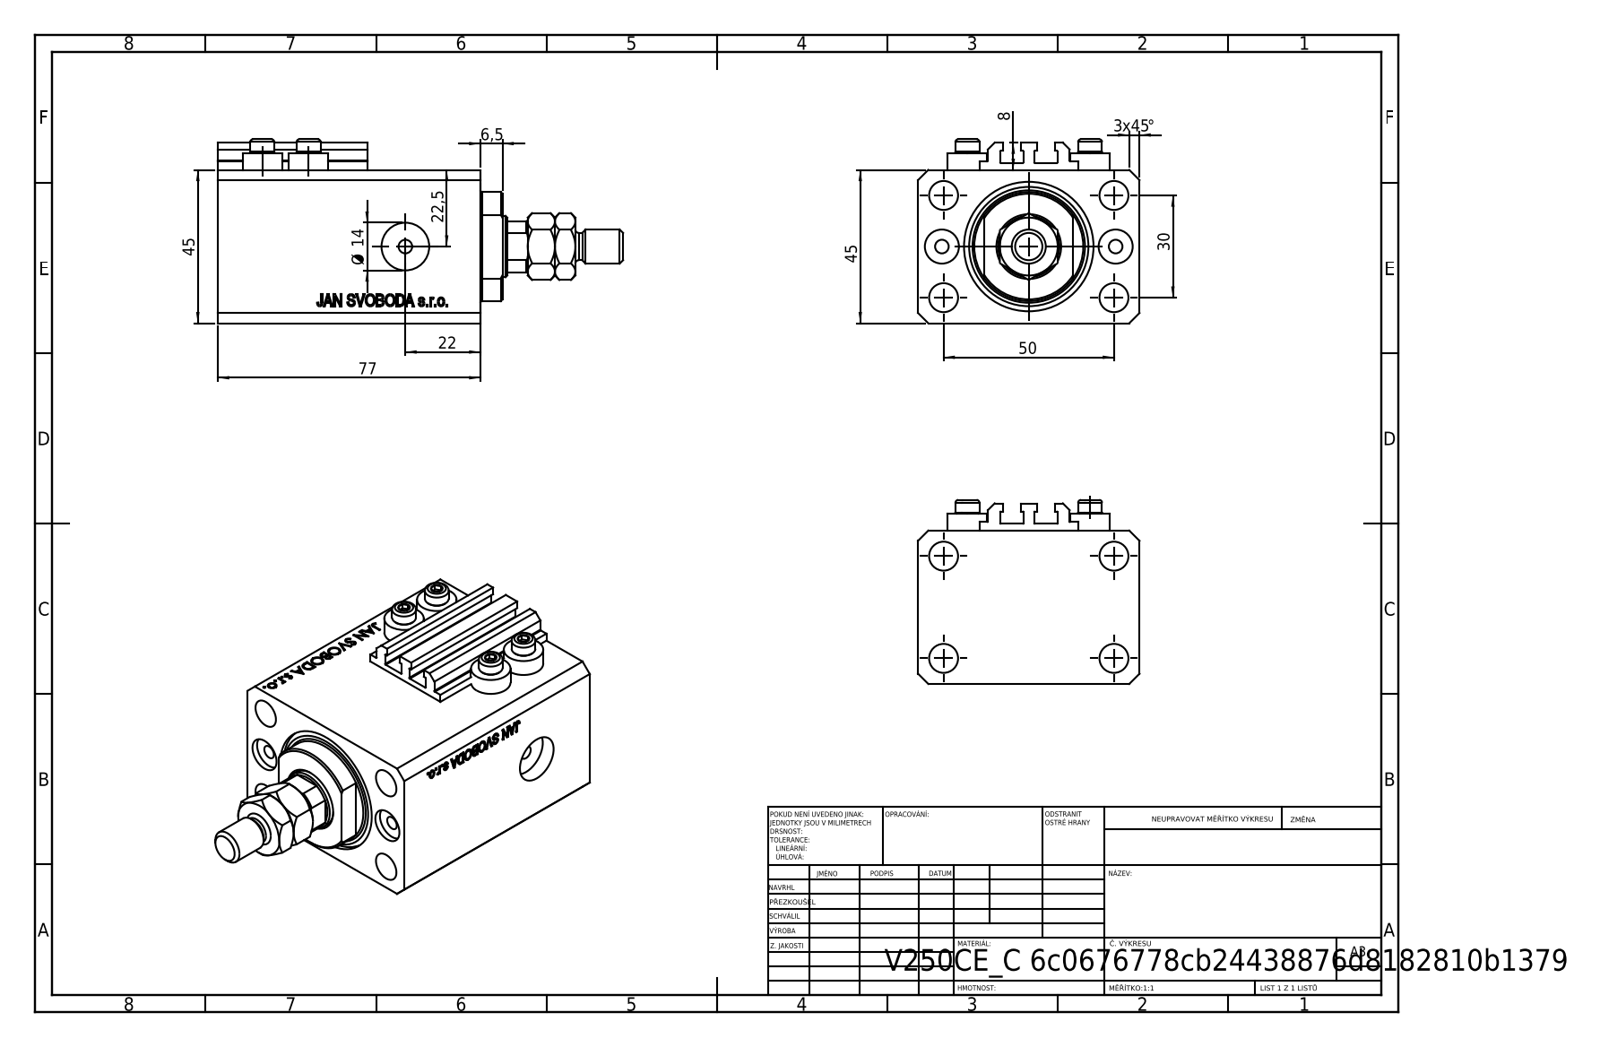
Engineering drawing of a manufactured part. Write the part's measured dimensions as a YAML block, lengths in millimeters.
part_name: "V250CE_C_VCP; V250CE_VC_C; ALLEN BOLT V250CE; V250CE_C (+1 more)"
step_written_by: "SolidWorks 2019 (CONFIG_CONTROL_DESIGN)"
units: millimeters
bodies: {solids: 9, faces: 1082, planar: 518, cylindrical: 90, other: 474}
overall_size: [118.9, 65, 54]
volume: 216375
surface_area: 61162
round_holes:
  - {diameter: 4, count: 8}
  - {diameter: 8.5, count: 5}
  - {diameter: 10, count: 2}
  - {diameter: 14, count: 2}
  - {diameter: 18, count: 1}
  - {diameter: 25, count: 1}
  - {diameter: 38, count: 1}
round_bosses_or_shafts:
  - {diameter: 11.6, count: 4}
  - {diameter: 7, count: 4}
  - {diameter: 10, count: 1}
  - {diameter: 8, count: 1}
partial_cylinders:
  - {radius: 0.2, count: 10}
  - {radius: 8.5, count: 1}
  - {radius: 16, count: 1}
face_to_face_distances: [45, 65, 51.9, 77, 25.1, 6.9, 70.1, 3, 47, 6]
hole_center_spacings: [15.01, 29.15, 52.68, 13.6, 25.5, 30, 36, 38.48]
